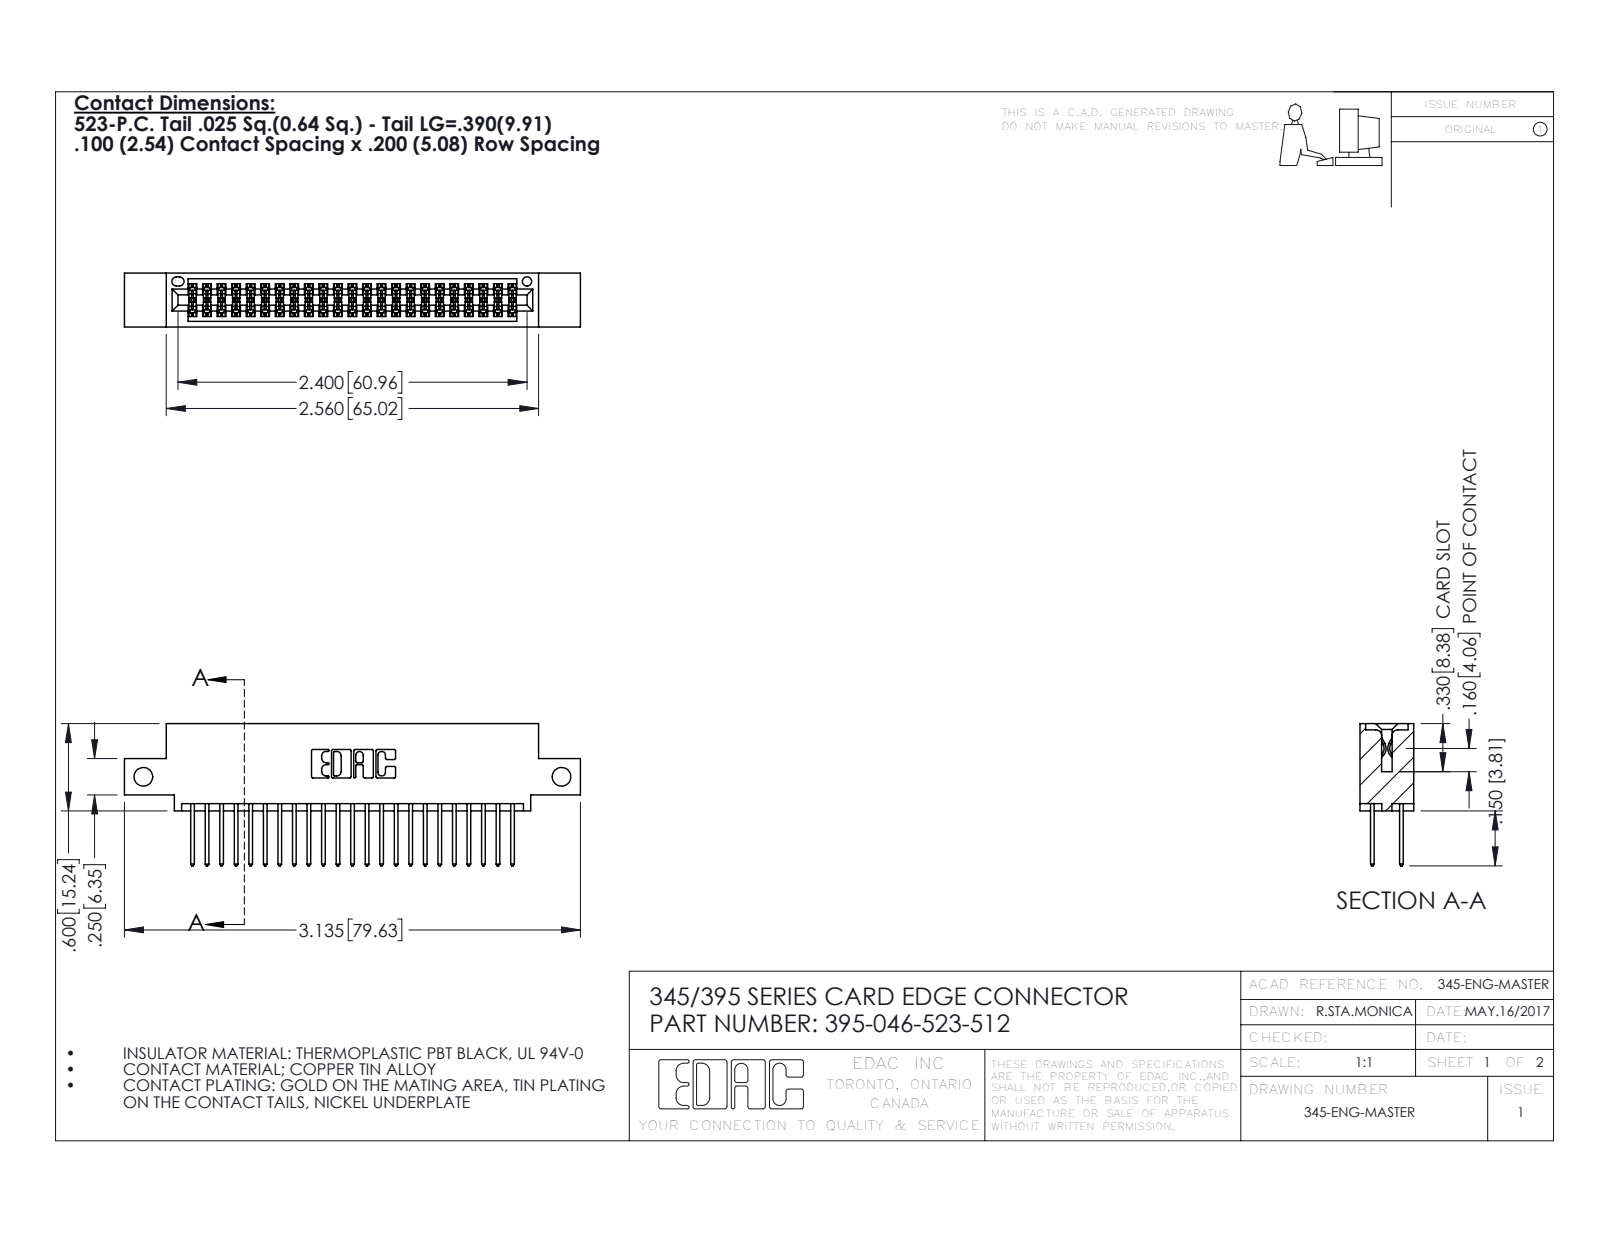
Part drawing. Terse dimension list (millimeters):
name: 345-292-001_345-293-123; 395-046-523-512; 345 Part_0.110 Offset - Side Mount
written by: SolidWorks 2016 (CONFIG_CONTROL_DESIGN)
unit: mm
bodies: 47 solids, 2430 faces (1602 planar, 828 cylindrical, 0 other)
size: 79.6 × 24.8 × 9.4
volume: 7 490 mm³; area: 11 090 mm²
holes: 2× ⌀3.3, 1× ⌀1.6
rounds: 69× R0.2, 46× R0.3, 22× R0.3, 6× R0.2, 6× R0.8, 3× R0.7, 2× R0.4, 2× R0.5
face distances: 7.6, 1.8, 5.1, 2.5, 6.9, 0.6, 9.4, 5.7, 4.4, 3.8
hole spacings: 73
